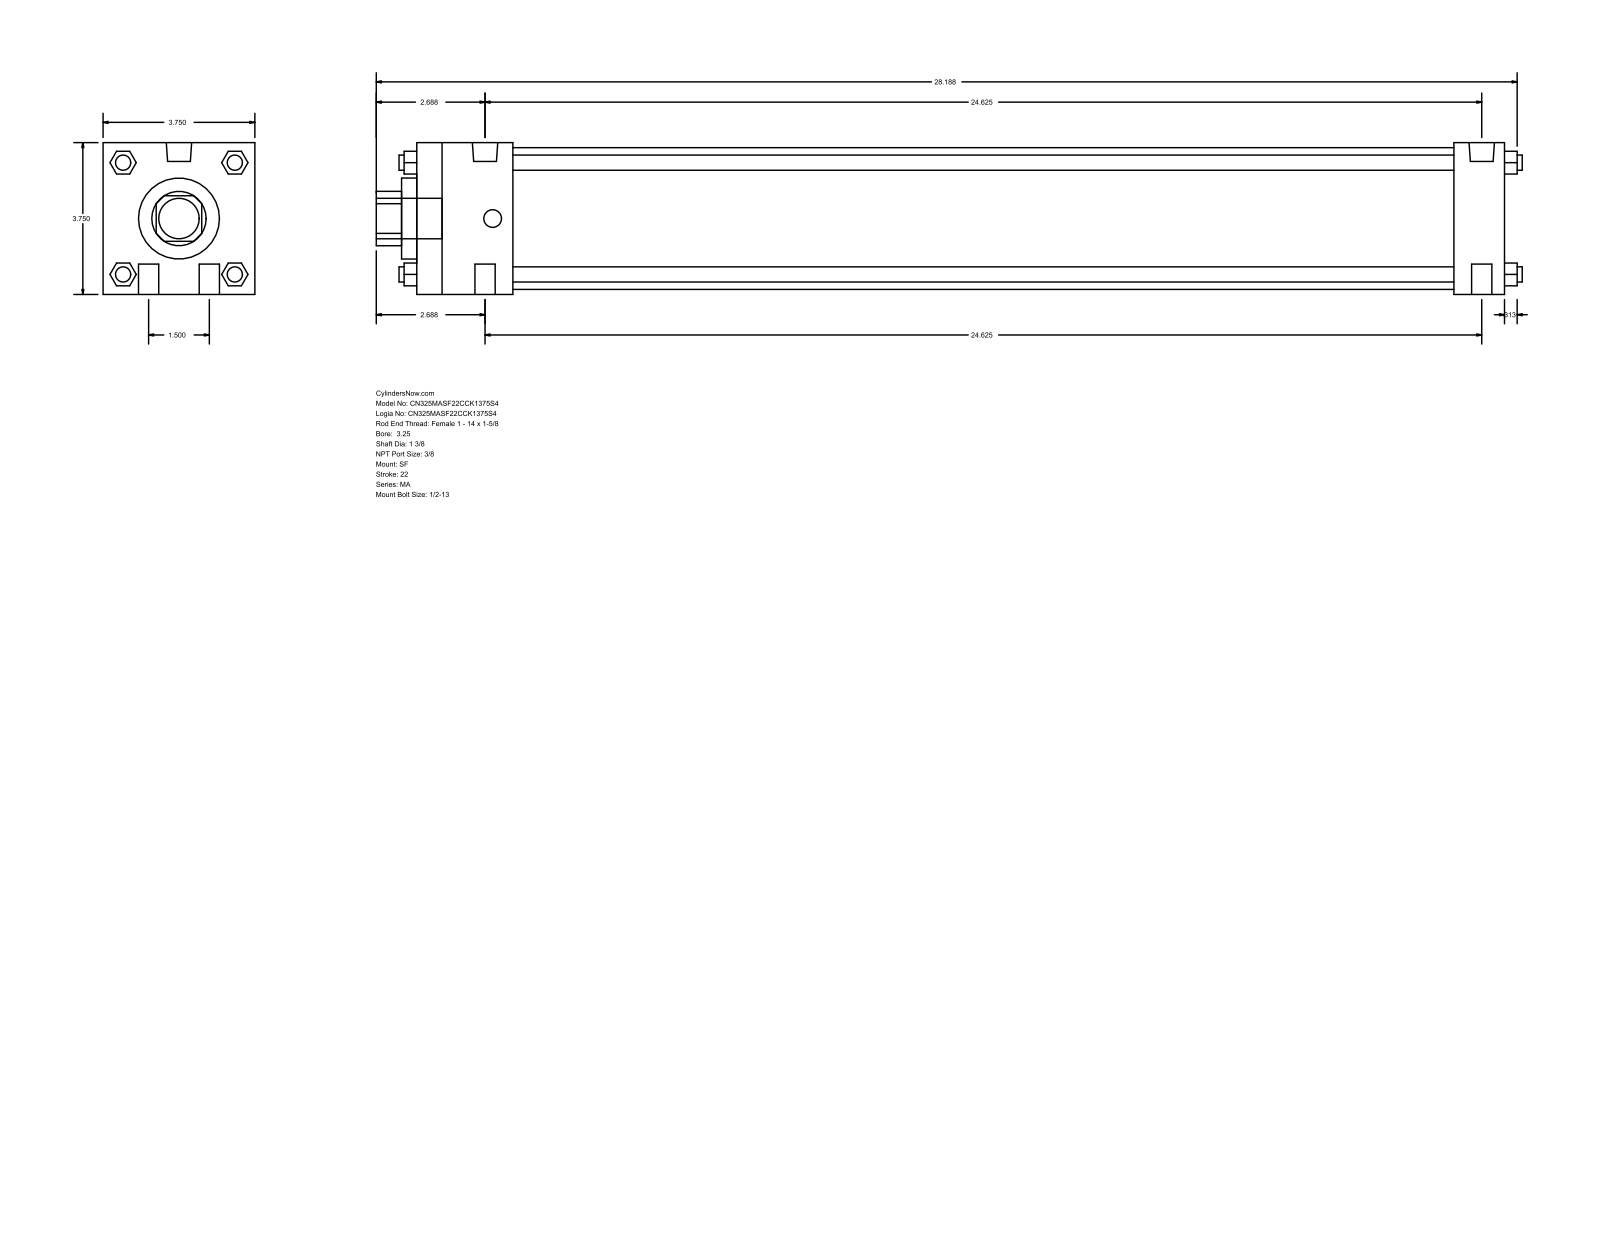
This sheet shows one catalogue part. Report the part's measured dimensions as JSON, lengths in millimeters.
{"part_name": "MA_SF__0325_1.375", "step_written_by": "GSSL Pune (CONFIG_CONTROL_DESIGN)", "units": "millimeters", "bodies": {"solids": 0, "faces": 124, "planar": 94, "cylindrical": 30, "other": 0}, "overall_size": [719.14, 95.25, 95.25], "round_holes": [[34.92, 1], [50.8, 1], [88.9, 1]], "round_bosses_or_shafts": [[12.7, 4], [9.53, 4], [15.93, 2], [11.11, 2], [25.4, 1]], "partial_cylinders_radius": [[17.06, 1]], "face_to_face_distances": [95.24, 682.62, 650.87, 31.75, 60.32, 590.55, 622.3, 9.52, 69.84, 660.39]}
